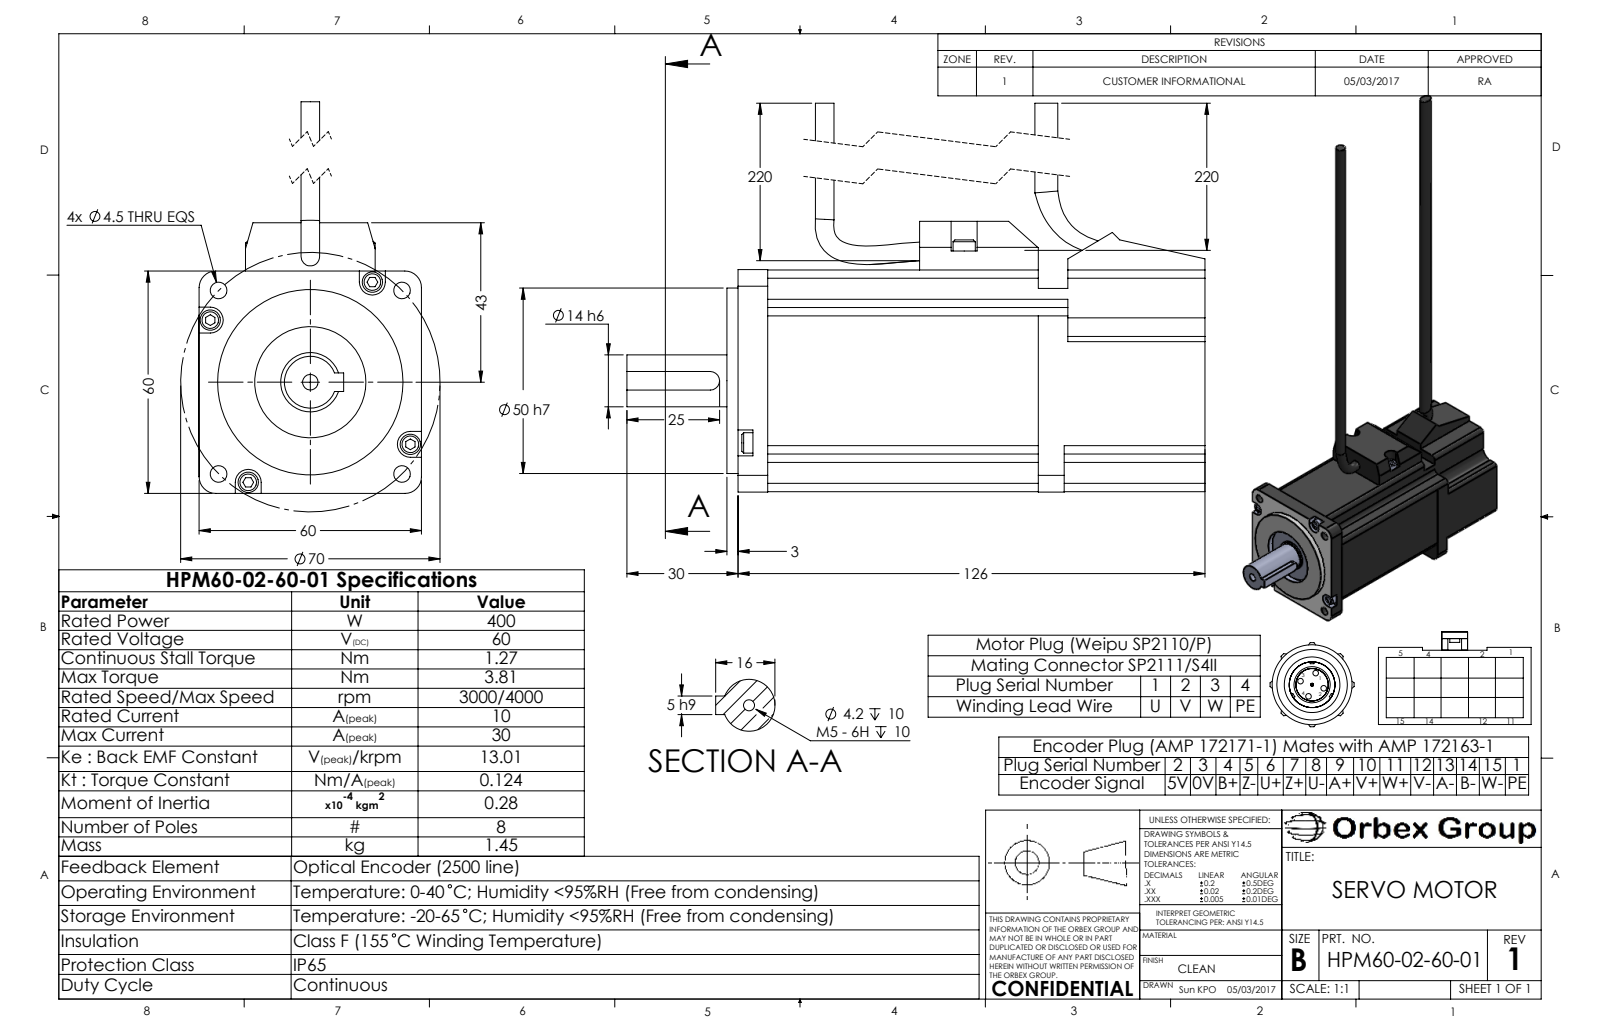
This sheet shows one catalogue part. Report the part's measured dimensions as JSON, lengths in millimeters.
{"part_name": "HPM60-02-60-01 Rev 1", "step_written_by": "SolidWorks 2015 (AUTOMOTIVE_DESIGN)", "units": "millimeters", "bodies": {"solids": 1, "faces": 220, "planar": 130, "cylindrical": 68, "other": 22}, "overall_size": [279.9, 156, 60.1], "volume_mm3": 431179, "surface_area_mm2": 49596, "round_holes": [[4.5, 4], [4.2, 1], [30, 1]], "round_bosses_or_shafts": [[5.5, 4], [6, 2], [50, 1], [16, 1], [14, 1]], "partial_cylinders_radius": [[2.25, 14], [3.5, 6], [4.5, 4], [5, 2], [2.5, 1]], "face_to_face_distances": [60, 49.65, 10.15, 39.5, 59.8, 126, 10.25, 49.75, 59.9, 10.35], "hole_center_spacings": [35, 49.5, 70]}
